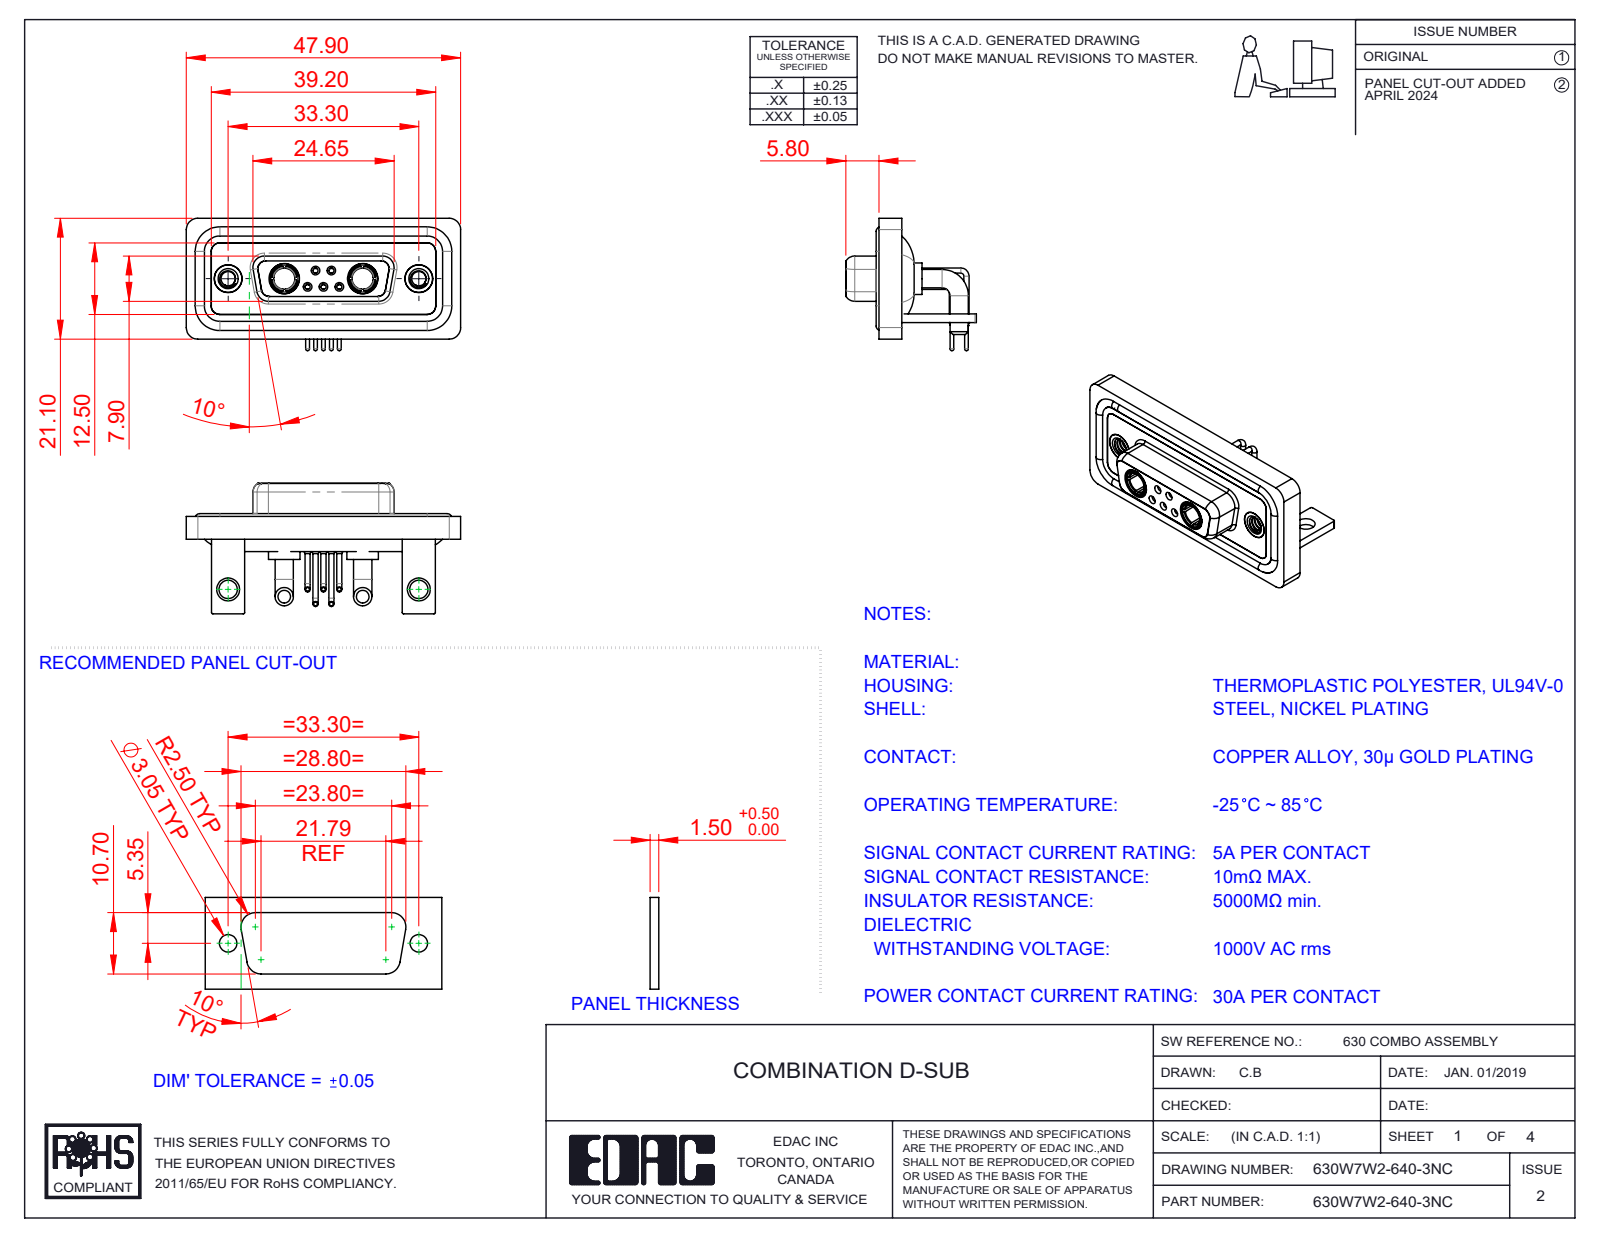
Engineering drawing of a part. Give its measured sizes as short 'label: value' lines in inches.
name: 630Combo Contact Row 1_50 Contacts; Power Socket_30A RA; 630Combo Contact Row 2_50 Contacts; 630Combo Threaded Rivet_A (+6 more)
written by: SolidWorks 2023 (CONFIG_CONTROL_DESIGN)
unit: in
bodies: 18 solids, 849 faces (258 planar, 375 cylindrical, 216 other)
size: 1.886 × 0.91 × 0.898
volume: 0.403 in³; area: 17.02 in²
holes: 5× ⌀0.035, 5× ⌀0.043, 5× ⌀0.059, 5× ⌀0.079, 4× ⌀0.191, 3× ⌀0.063, 2× ⌀0.067, 2× ⌀0.098, 2× ⌀0.126, 2× ⌀0.146, 2× ⌀0.157, 2× ⌀0.159
bosses: 6× ⌀0.063, 5× ⌀0.035, 5× ⌀0.026, 4× ⌀0.126, 2× ⌀0.217, 2× ⌀0.205, 2× ⌀0.195, 2× ⌀0.195
rounds: 21× R0.079, 18× R0.059, 16× R0.01, 12× R0.053, 8× R0.063, 5× R0.02, 4× R0.024, 4× R0.026
face distances: 0.016, 0.114, 0.059, 0.071, 0.146, 0.043, 0.161, 0.063, 0.098, 0.055
hole spacings: 0.124, 0.109, 0.386, 0.925, 1.311, 0.17, 0.17, 0.198
